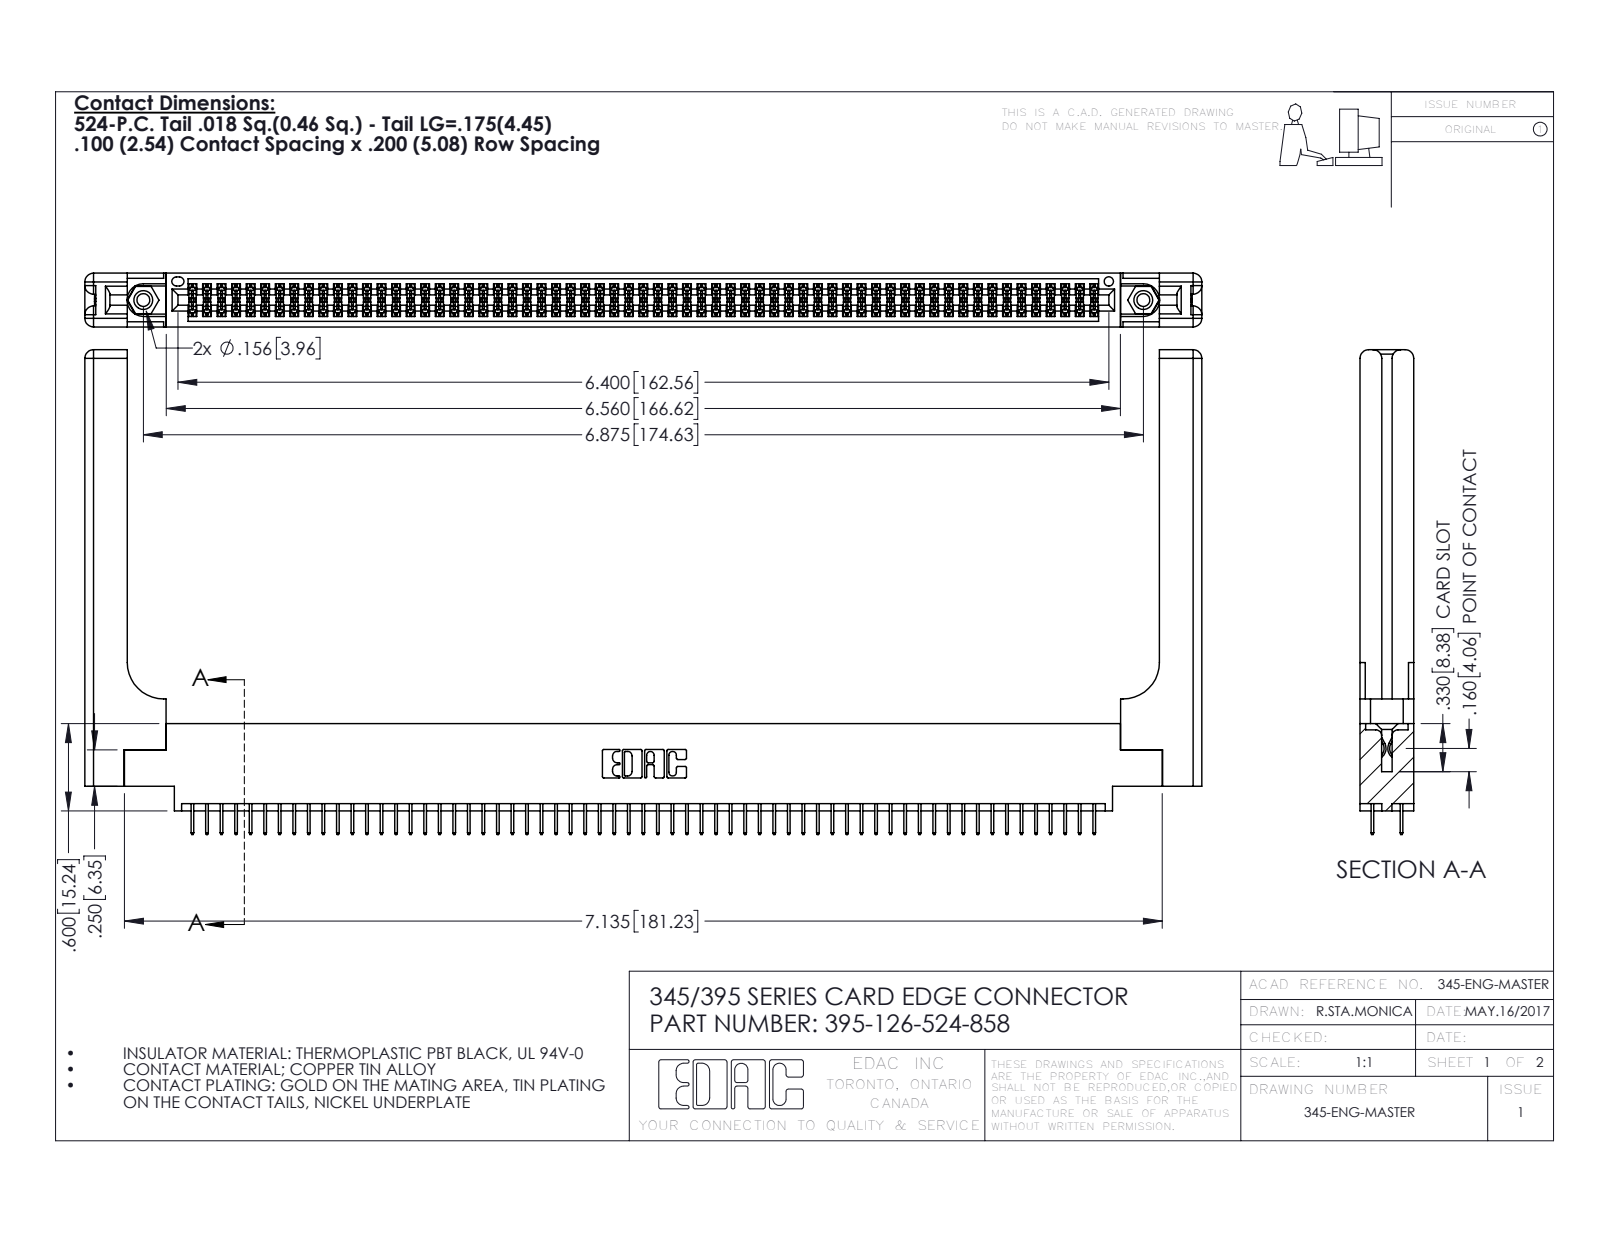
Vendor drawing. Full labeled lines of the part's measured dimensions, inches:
Part name (STEP PRODUCT): 345 Part_0.170 Offset - 0.156 Dia-TH; 345-220-058_345-220-058; 395-126-524-858; 345-250-001_345-250-001-102 (+1 more)
STEP written by: SolidWorks 2016 (CONFIG_CONTROL_DESIGN)
Units: inches
Bodies: 131 solids, 7190 faces (5146 planar, 1984 cylindrical, 60 other)
Overall size (bounding box): 7.679 × 3.332 × 0.37
Volume: 1.667 in³ · Surface area: 51.07 in²
Round holes (diameter × count): ⌀0.089 ×2, ⌀0.125 ×2, ⌀0.156 ×2, ⌀0.064 ×1
Round bosses / shafts (diameter × count): ⌀0.155 ×2
Partial cylindrical surfaces — rounded edges, fillets, slot ends (radius × count): R0.006 ×189, R0.01 ×22, R0.06 ×16, R0.007 ×6, R0.031 ×6, R0.026 ×3, R0.014 ×2, R0.019 ×2
Main face-to-face distances: 0.072, 0.37, 0.298, 0.2, 0.098, 0.272, 0.025, 0.225, 0.175, 0.072
Hole centre spacings: 0.27, 6.639, 6.875
